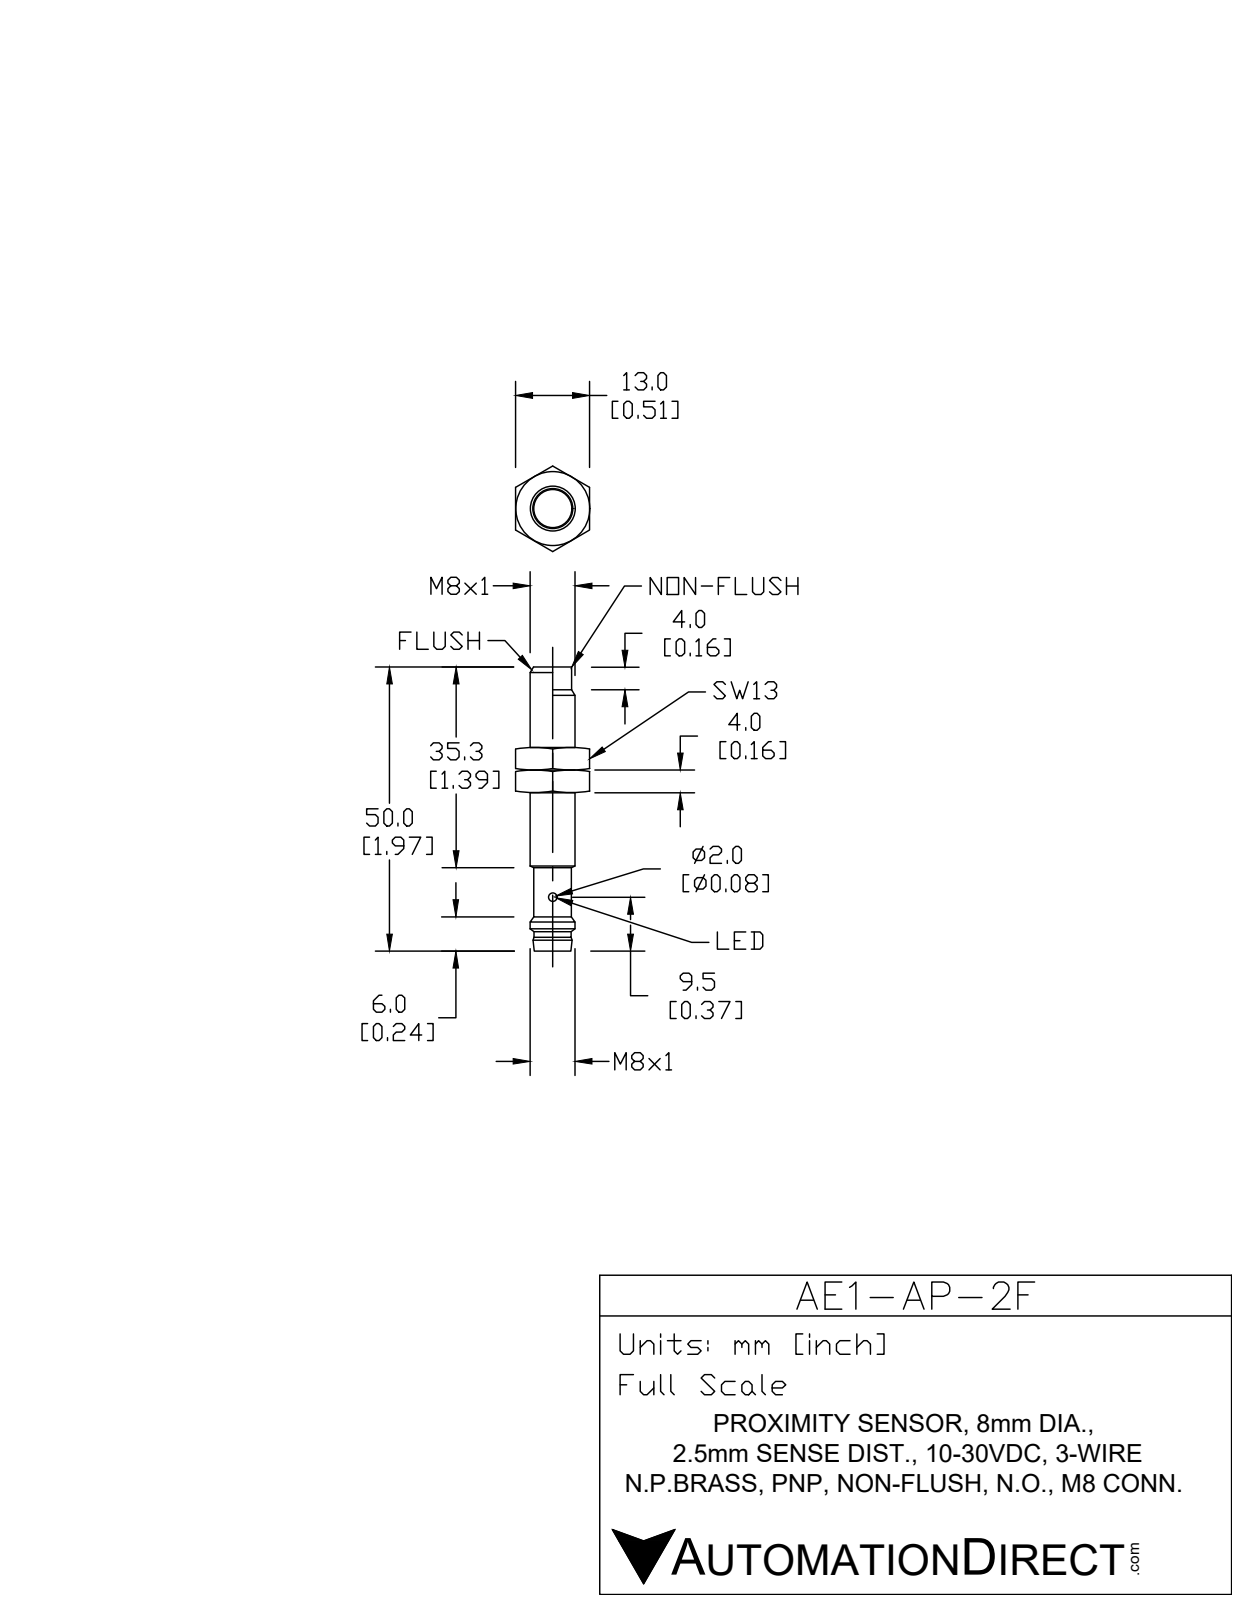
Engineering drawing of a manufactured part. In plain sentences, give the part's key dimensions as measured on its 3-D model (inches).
The part is named "AE1-AP-2F". Its 3-D file was written by "SolidWorks 2017 (AUTOMOTIVE_DESIGN)". It is 3 solids with 61 faces: 11 planar, 30 cylindrical and 20 other. Overall it measures 1.976 by 0.315 by 0.315 inches. Its volume is 0.139 cubic inches and its surface area 2.574 square inches. Round holes: 2 of diameter 0.079, 1 of diameter 0.228. Round bosses or shafts: 3 of diameter 0.039, 1 of diameter 0.315, 1 of diameter 0.272, 1 of diameter 0.256, 1 of diameter 0.23. The main face-to-face distances are 1.622, 0.157, 1.78, 1.524, 1.366, 0.256, 1.976, 1.819, 0.453, 0.197.
